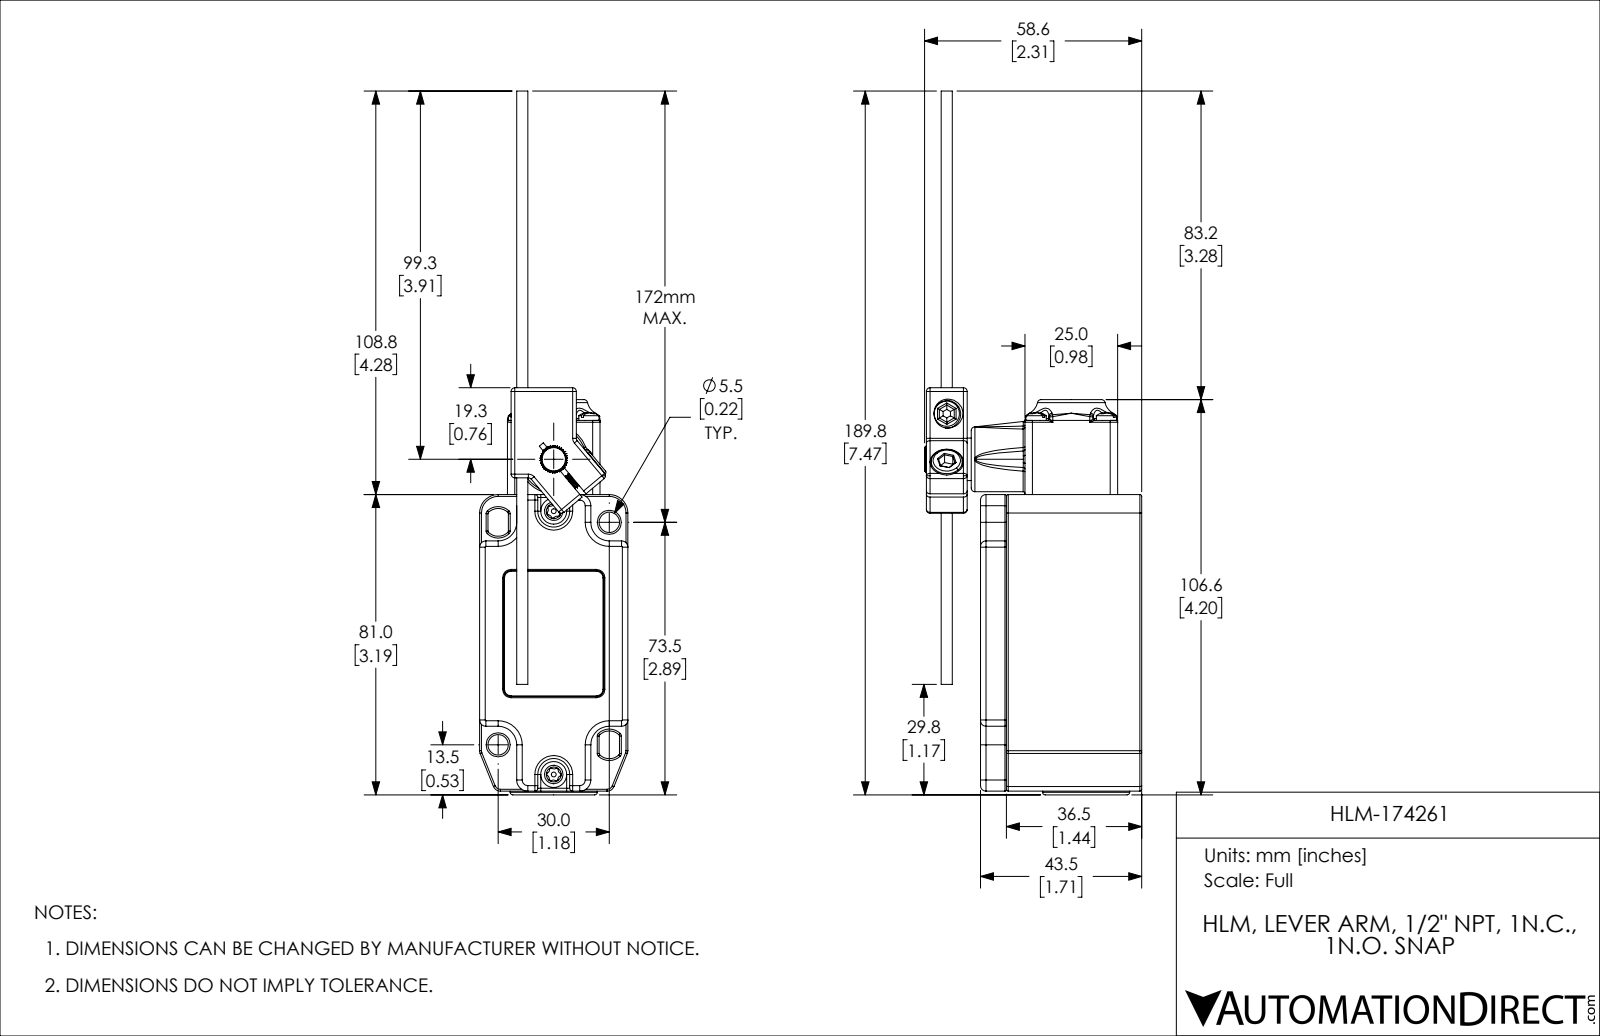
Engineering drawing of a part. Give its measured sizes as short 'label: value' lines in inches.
name: 174-HLM (Lever Arm) (STEP format)
written by: SolidWorks 2015 (CONFIG_CONTROL_DESIGN)
unit: in
bodies: 15 solids, 3082 faces (749 planar, 766 cylindrical, 1567 other)
size: 7.472 × 2.307 × 1.575
volume: 4.433 in³; area: 84.07 in²
holes: 11× ⌀0.118, 4× ⌀0.106, 4× ⌀0.134, 3× ⌀0.217, 2× ⌀0.146, 2× ⌀0.15, 2× ⌀0.157, 2× ⌀0.165, 2× ⌀0.571, 1× ⌀0.138, 1× ⌀0.169, 1× ⌀0.173
bosses: 6× ⌀0.244, 4× ⌀0.216, 2× ⌀0.276, 2× ⌀0.252, 2× ⌀0.051, 1× ⌀0.925, 1× ⌀0.728, 1× ⌀0.697
rounds: 166× R0.02, 54× R0.039, 26× R0.016, 14× R0.006, 12× R0.012, 12× R0.079, 10× R0.031, 9× R0.059
face distances: 0.089, 1.486, 1.575, 0.098, 1.398, 1.512, 0.102, 1.713, 1.61, 0.173
hole spacings: 0.748, 0.529, 1.258, 0.354, 0.432, 0.65, 0.75, 0.828
